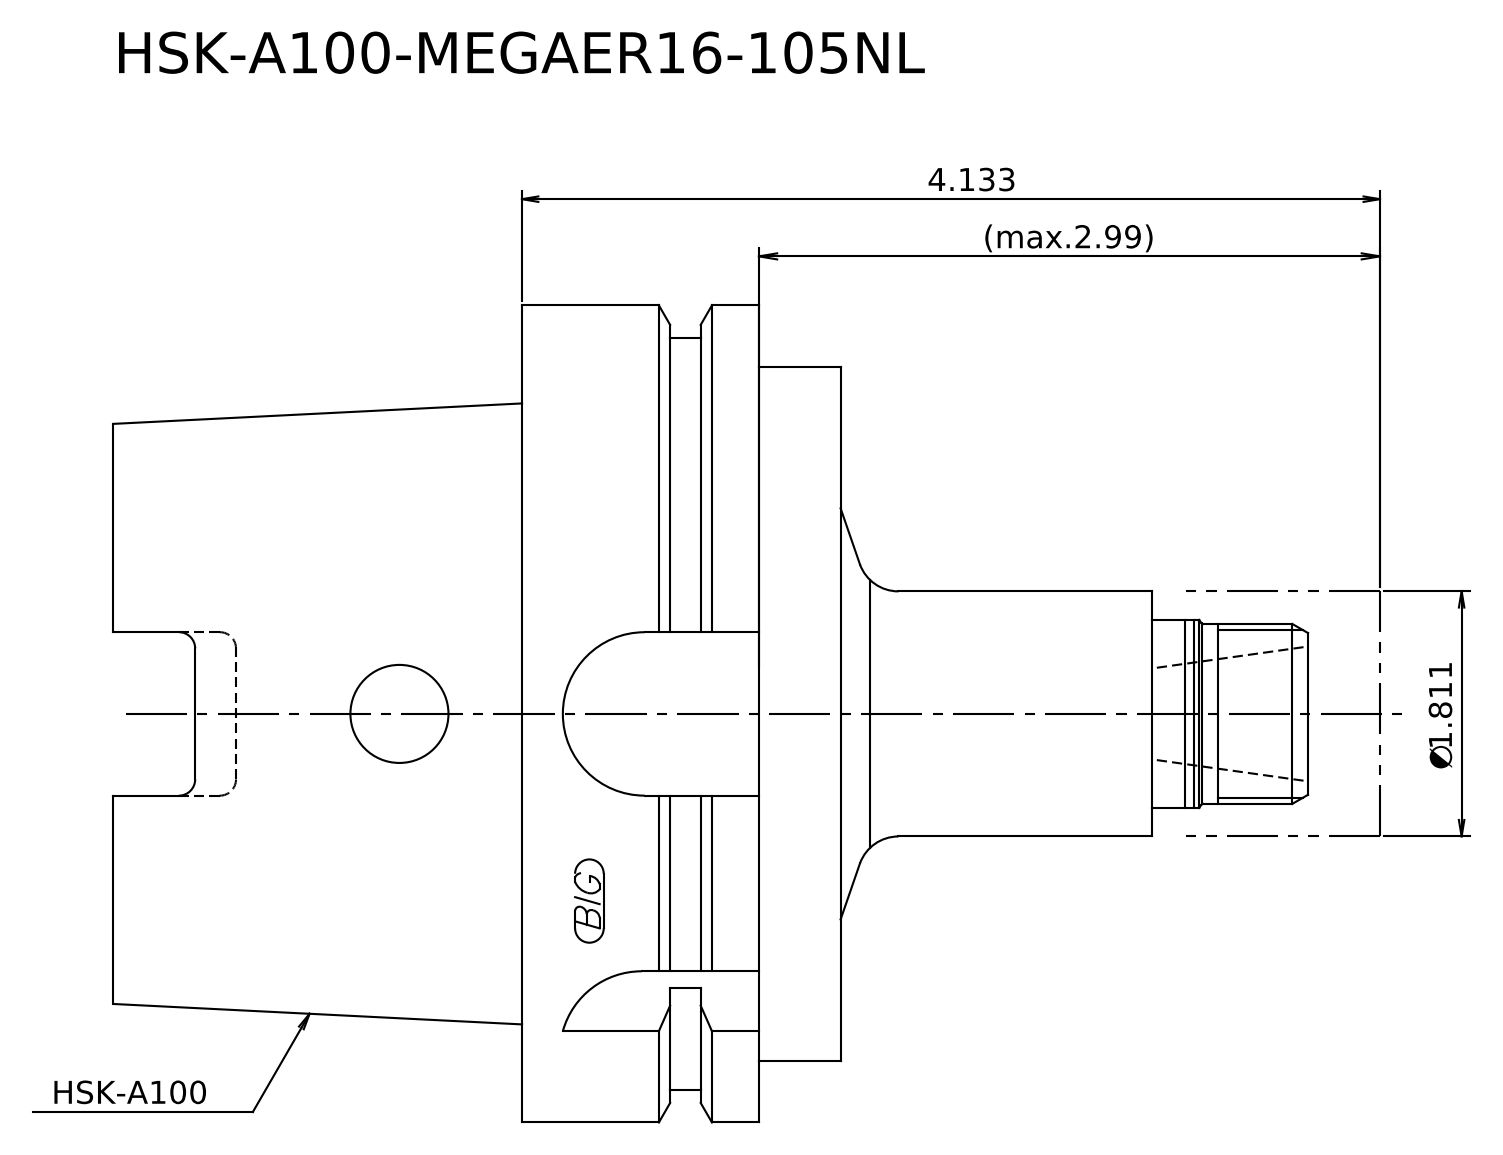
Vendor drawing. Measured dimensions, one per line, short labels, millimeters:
written by: Kubotek KeyCreator 2011 V10.0.2 (22737) (automotive_design)
unit: mm
bodies: 2 solids, 24 faces (10 planar, 8 cylindrical, 6 other)
size: 155 × 100 × 100
volume: 547 351 mm³; area: 48 386 mm²
bosses: 1× ⌀100, 1× ⌀92, 1× ⌀85, 1× ⌀30, 1× ⌀23, 1× ⌀22
face distances: 89, 39, 50, 10, 29, 79, 41, 51, 80, 130
